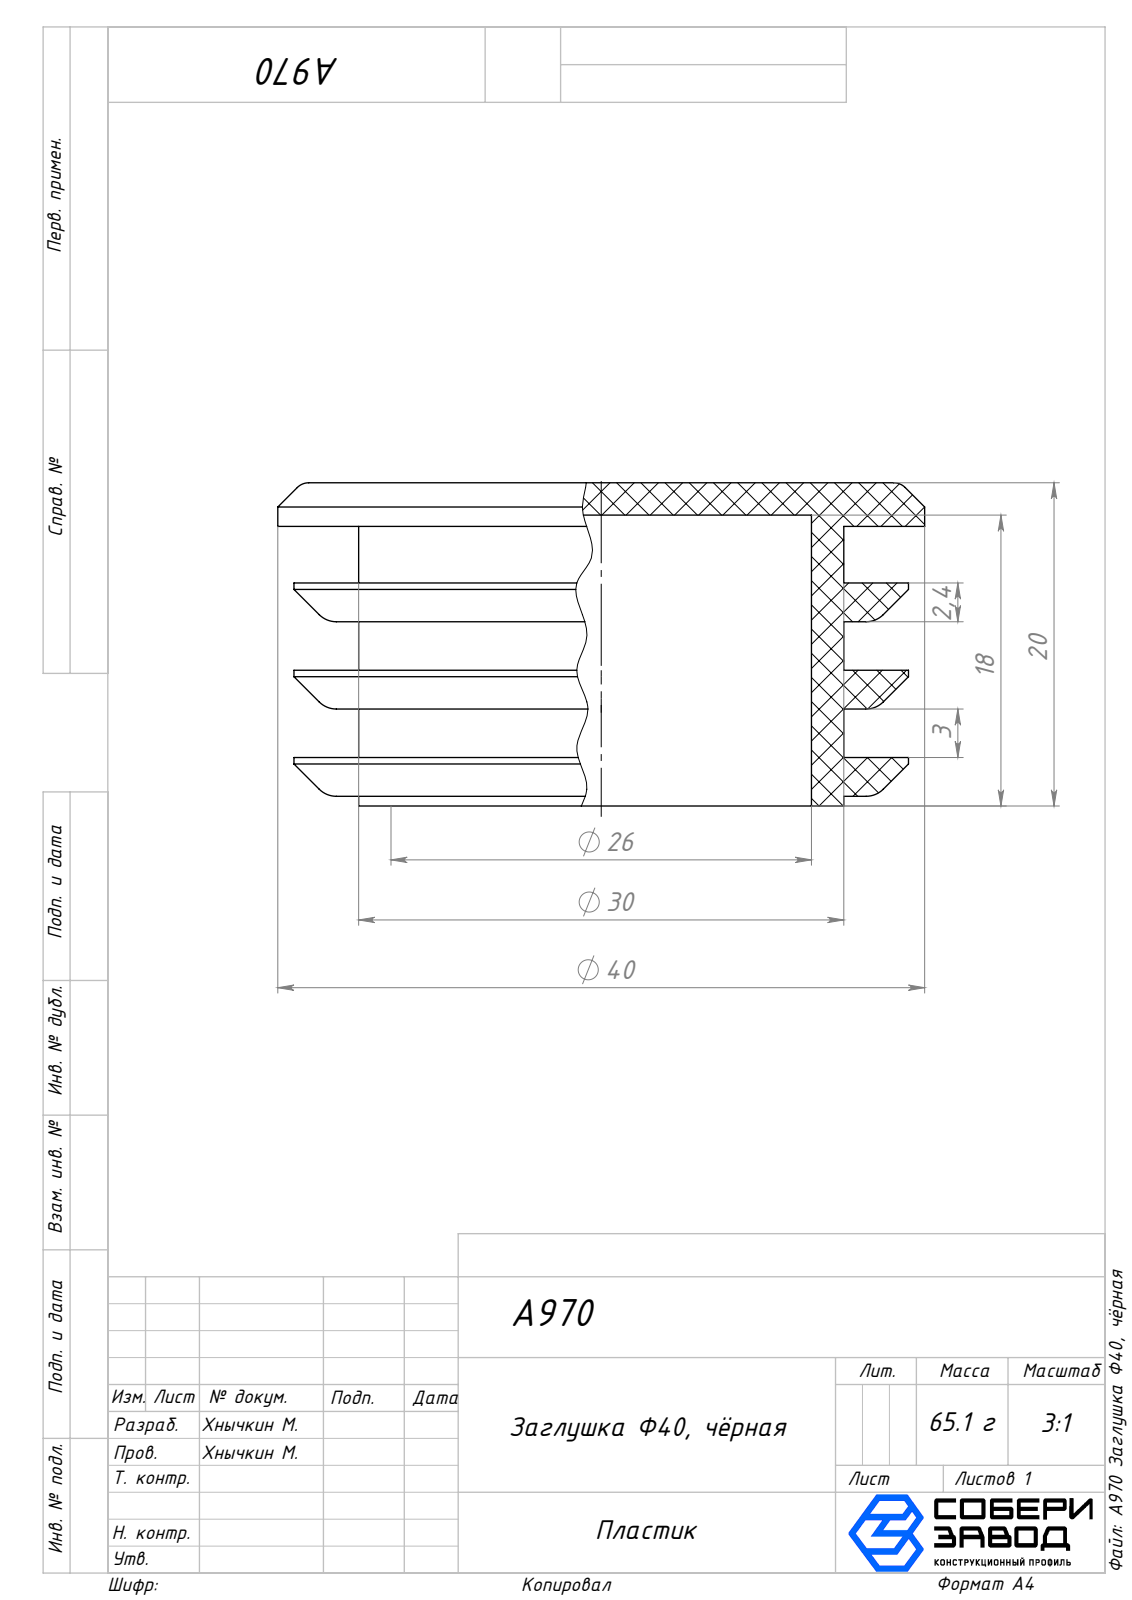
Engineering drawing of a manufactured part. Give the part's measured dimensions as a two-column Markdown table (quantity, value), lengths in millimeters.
| quantity | value |
| --- | --- |
| part name | A970 Заглушка Ф40, чёрная |
| STEP written by | SolidWorks 2025 (AUTOMOTIVE_DESIGN) |
| units | millimeters |
| bodies | 1 solid, 44 faces (10 planar, 18 cylindrical, 16 other) |
| overall size | 40 × 40 × 20 |
| volume | 8 294 mm³ |
| surface area | 8 123 mm² |
| round holes (diameter × count) | 26 × 1 |
| round bosses / shafts (diameter × count) | 40 × 1, 38 × 1, 30 × 1 |
| main face-to-face distances | 5.4, 10.8, 2.7, 0.7, 2, 3, 8.9, 9.6, 11.6, 14.3 |
